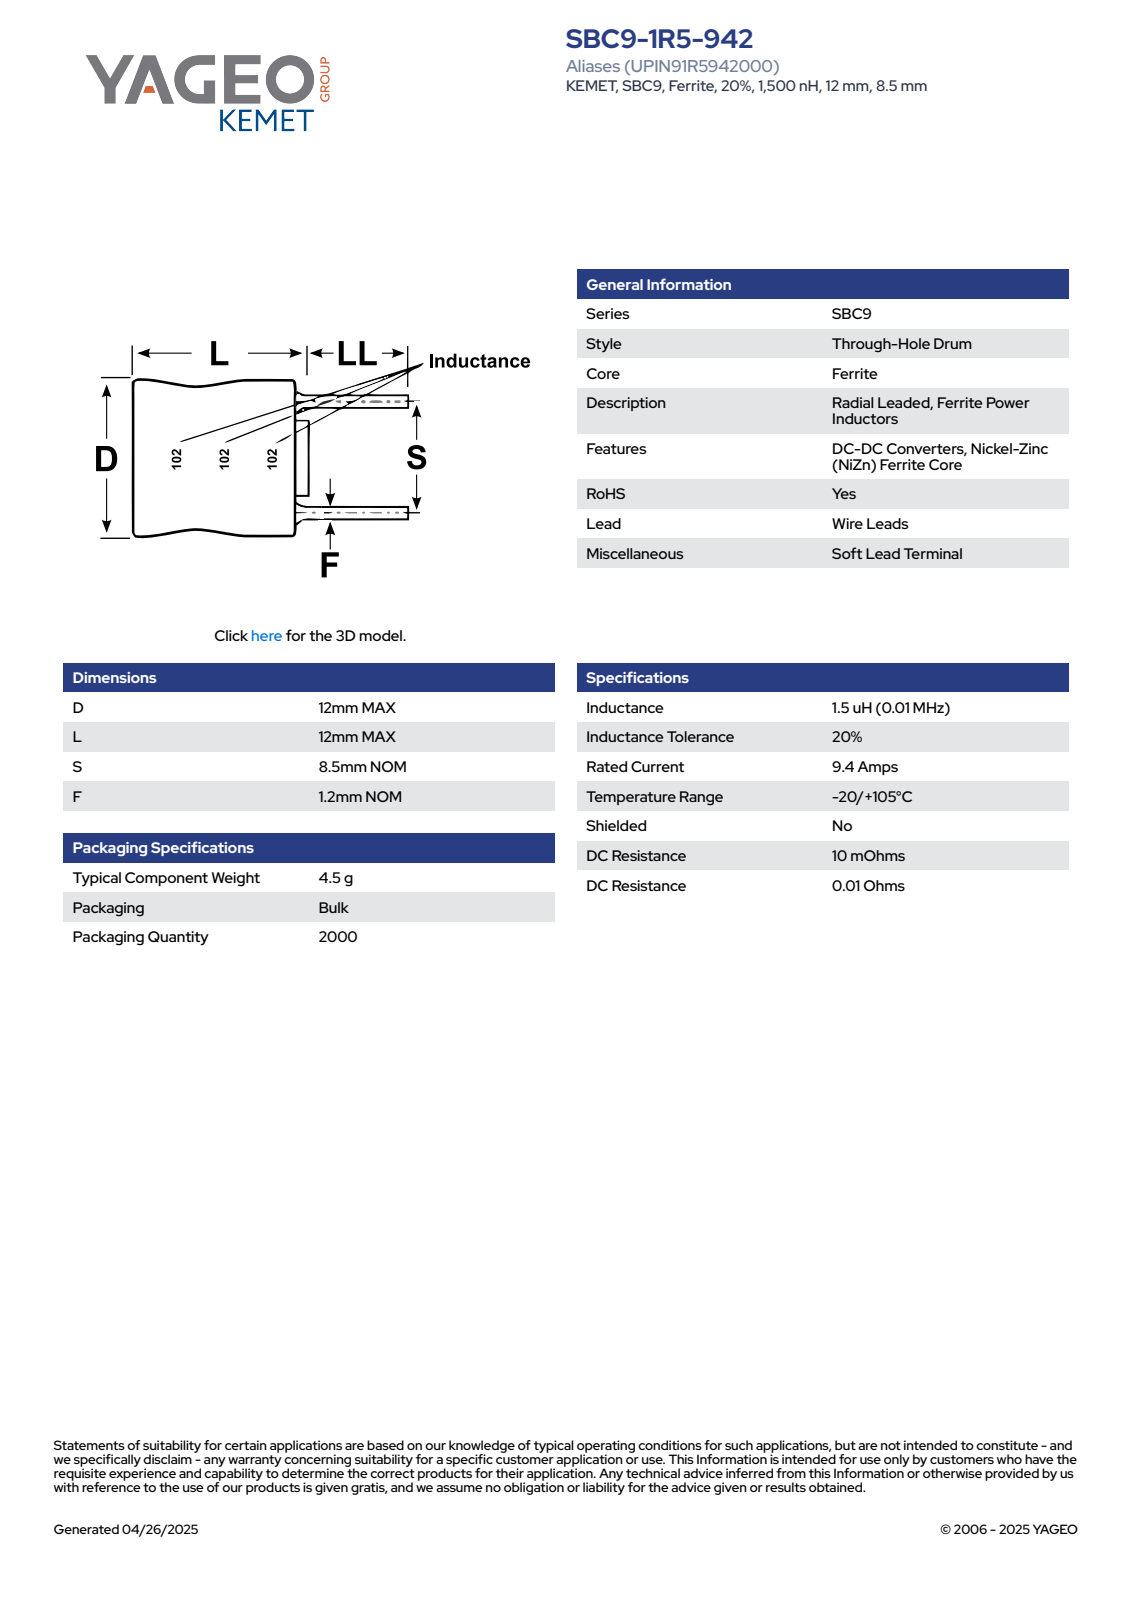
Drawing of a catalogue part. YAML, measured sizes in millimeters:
part_name: "IL_SBCP_D12L12S8.5LL4.5F1.2"
step_written_by: "SolidWorks 2014 (AUTOMOTIVE_DESIGN)"
units: millimeters
bodies: {solids: 4, faces: 84, planar: 66, cylindrical: 10, other: 8}
overall_size: [16.5, 12, 12]
volume: 1190
surface_area: 700
round_bosses_or_shafts:
  - {diameter: 1.2, count: 2}
  - {diameter: 12, count: 1}
  - {diameter: 10.92, count: 1}
face_to_face_distances: [11.65, 4.85, 16.5, 4.5, 0.35, 12, 5.66, 0.73, 1.03, 1.76]
